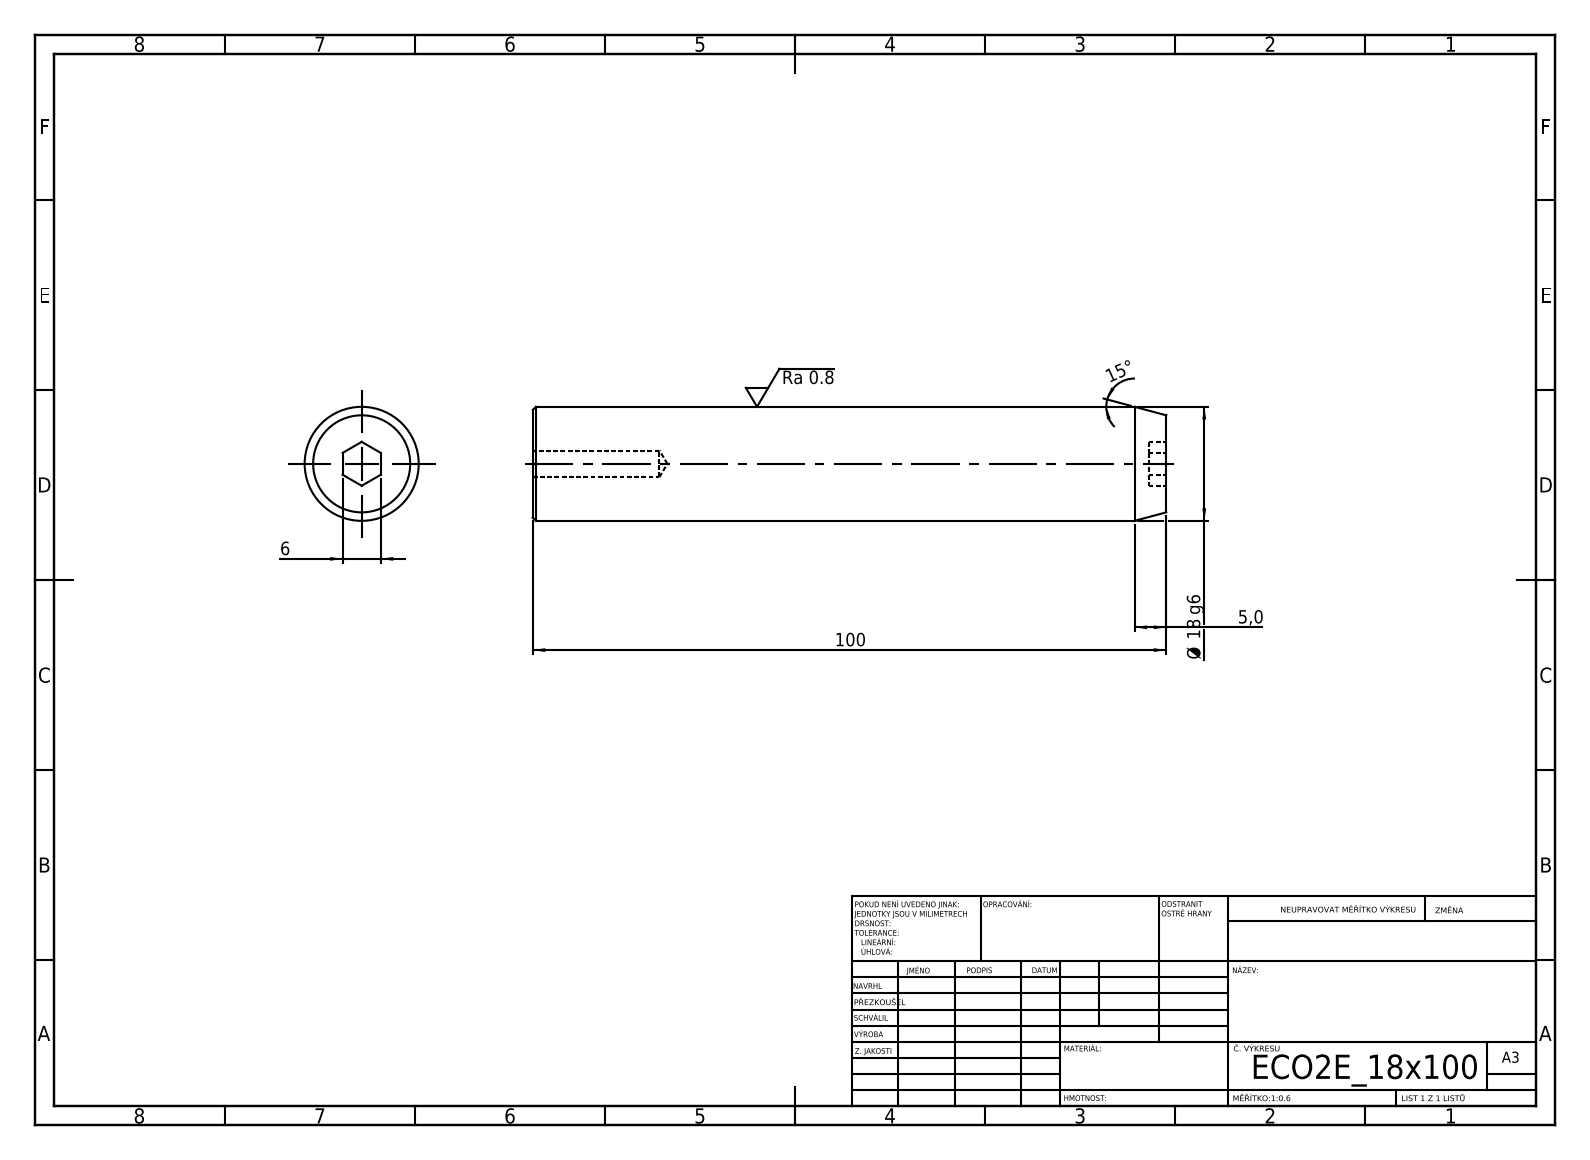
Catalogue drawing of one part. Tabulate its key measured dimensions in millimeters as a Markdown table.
| quantity | value |
| --- | --- |
| STEP written by | SolidWorks 2019 (CONFIG_CONTROL_DESIGN) |
| units | millimeters |
| bodies | 1 solid, 19 faces (9 planar, 4 cylindrical, 6 other) |
| overall size | 100 × 18 × 18 |
| volume | 24 890 mm³ |
| surface area | 6 389 mm² |
| round holes (diameter × count) | 4.2 × 1 |
| round bosses / shafts (diameter × count) | 18 × 1 |
| main face-to-face distances | 100, 2.8, 97.2, 6 |
